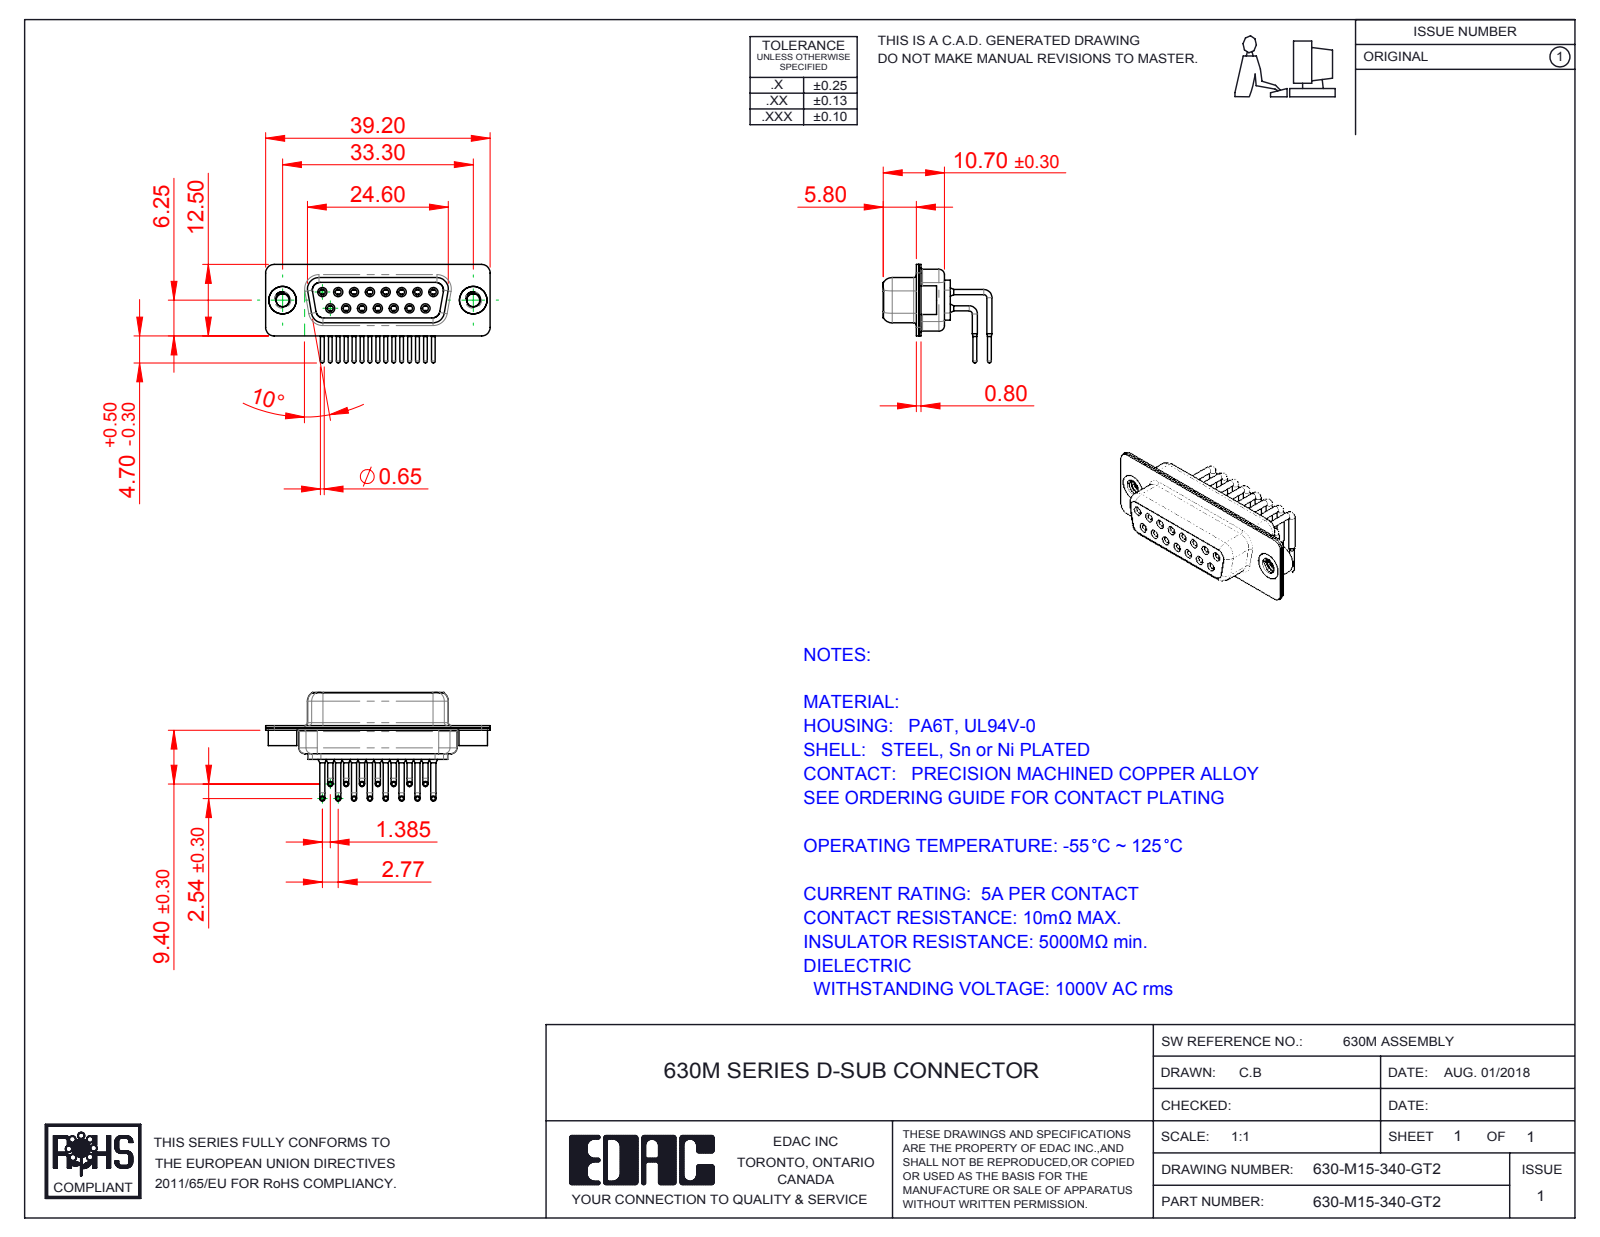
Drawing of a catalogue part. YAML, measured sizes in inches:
part_name: "630M 4-40 Threaded Rivet; 630M Shell Front_15 Contacts; 630M Contact Row 2; 630M Contact Row 1 (+3 more)"
step_written_by: "SolidWorks 2016 (CONFIG_CONTROL_DESIGN)"
units: inches
bodies: {solids: 20, faces: 1074, planar: 292, cylindrical: 482, other: 300}
overall_size: [1.543, 0.748, 0.677]
volume: 0.157
surface_area: 10.16
round_holes:
  - {diameter: 0.039, count: 15}
  - {diameter: 0.043, count: 15}
  - {diameter: 0.067, count: 15}
  - {diameter: 0.071, count: 15}
  - {diameter: 0.079, count: 15}
  - {diameter: 0.089, count: 2}
  - {diameter: 0.157, count: 2}
  - {diameter: 0.189, count: 2}
round_bosses_or_shafts:
  - {diameter: 0.035, count: 30}
  - {diameter: 0.063, count: 15}
  - {diameter: 0.059, count: 15}
  - {diameter: 0.026, count: 15}
  - {diameter: 0.197, count: 2}
  - {diameter: 0.193, count: 2}
partial_cylinders:
  - {radius: 0.059, count: 16}
  - {radius: 0.079, count: 12}
  - {radius: 0.053, count: 8}
  - {radius: 0.063, count: 8}
  - {radius: 0.01, count: 4}
  - {radius: 0.02, count: 4}
  - {radius: 0.024, count: 4}
  - {radius: 0.026, count: 4}
face_to_face_distances: [0.016, 0.057, 0.352, 0.091, 0.244, 0.031, 0.075, 0.335, 0.018, 0.278]
hole_center_spacings: [0.124, 0.109, 0.218, 0.327, 0.436, 0.198, 0.198, 0.294]
